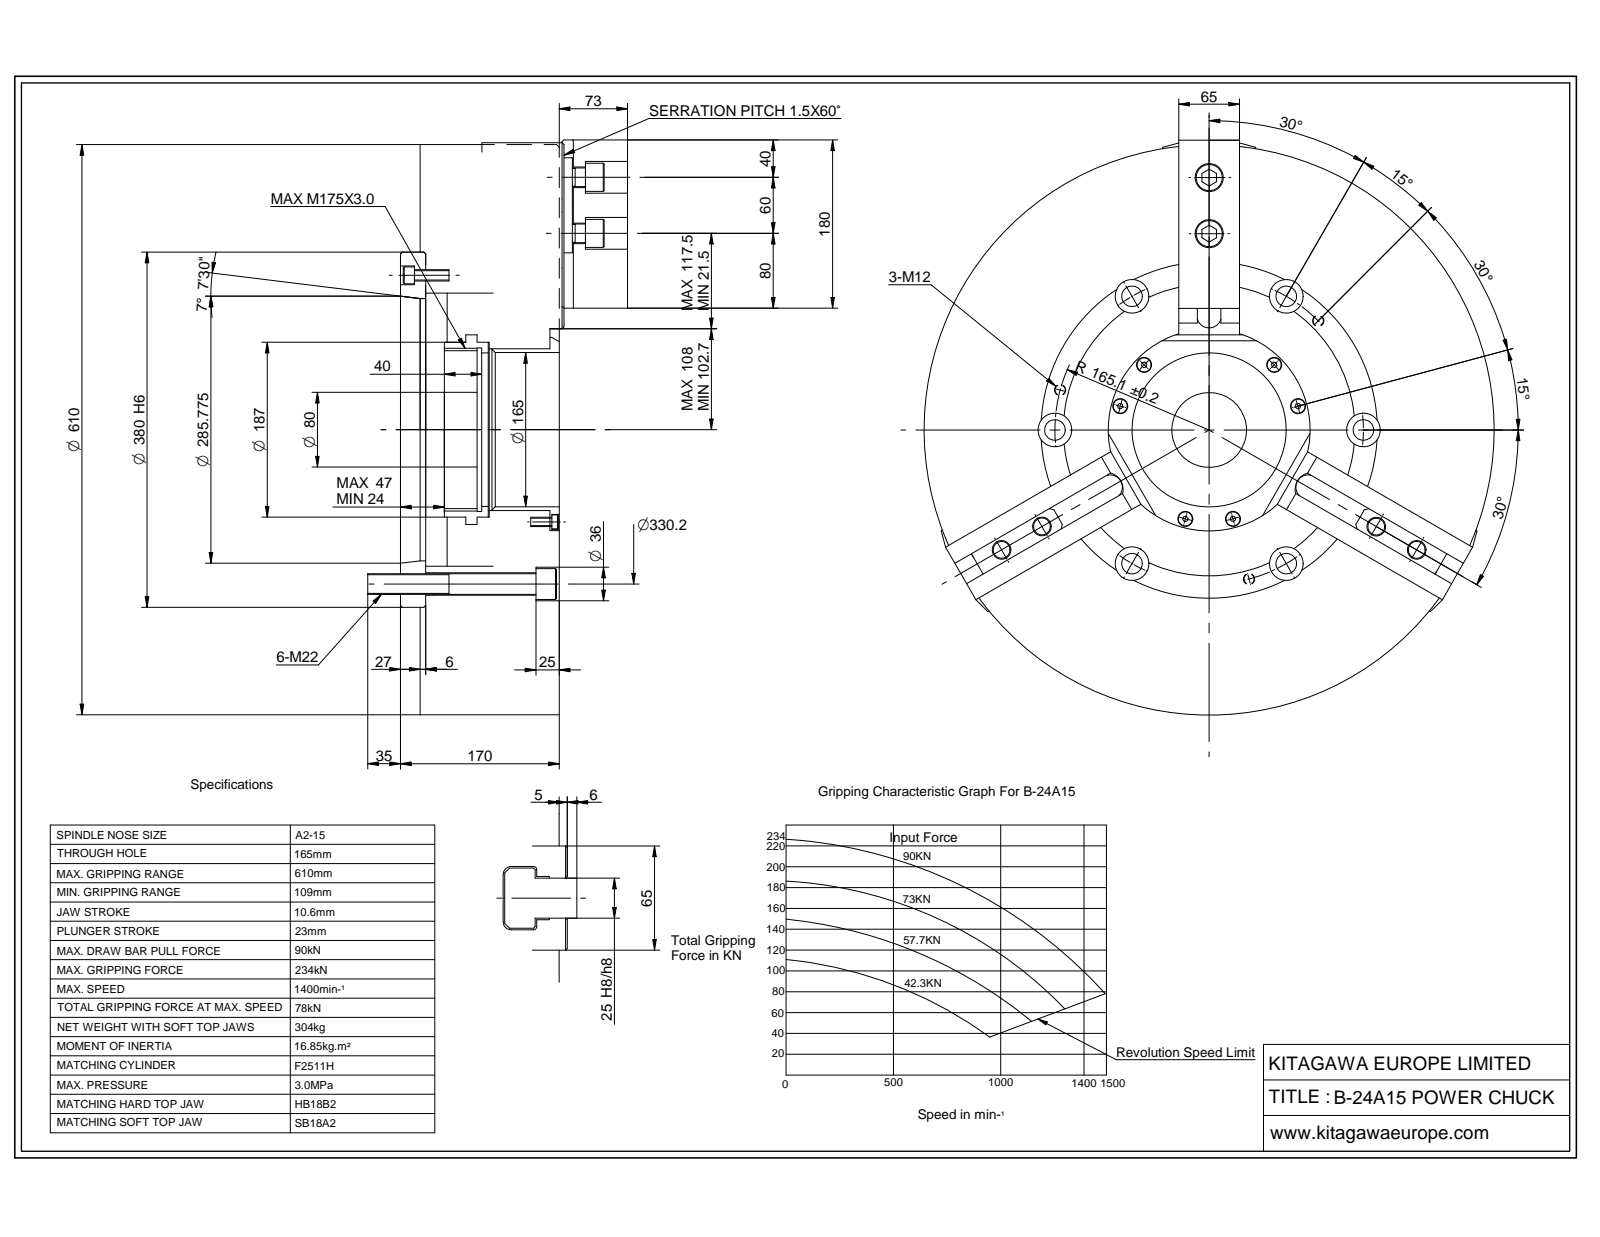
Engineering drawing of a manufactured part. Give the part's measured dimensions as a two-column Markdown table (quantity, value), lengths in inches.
| quantity | value |
| --- | --- |
| part name | B24A15; B24; CB-21A15 |
| STEP written by | ST-DEVELOPER v16 (AUTOMOTIVE_DESIGN) |
| units | inches |
| bodies | 2 solids, 4758 faces (3867 planar, 409 cylindrical, 482 other) |
| overall size | 24.769 × 24.016 × 10.945 |
| volume | 2 301 in³ |
| surface area | 3 446 in² |
| round holes (diameter × count) | 0.787 × 15, 1.969 × 12, 0.236 × 10, 0.398 × 9, 0.472 × 9, 0.531 × 9, 0.15 × 6, 0.194 × 6, 0.26 × 6, 0.433 × 6, 0.827 × 6, 0.945 × 6 |
| round bosses / shafts (diameter × count) | 1.299 × 6, 1.181 × 6, 0.787 × 6, 0.709 × 6, 0.394 × 6, 0.315 × 3, 24.016 × 1, 16.535 × 1 |
| partial cylindrical surfaces (radius × count) | 0.039 × 18, 0.018 × 12, 0.024 × 12, 0.031 × 12, 0.02 × 6, 0.071 × 6, 0.079 × 6, 0.122 × 6 |
| main face-to-face distances | 5.63, 0.236, 4.882, 1.811, 2.362, 1.063, 0.787, 0.827, 0.591, 5.866 |
| hole center spacings | 8.366, 14.778, 12.421, 16.707, 3.35, 4.37, 5.276, 5.903 |
